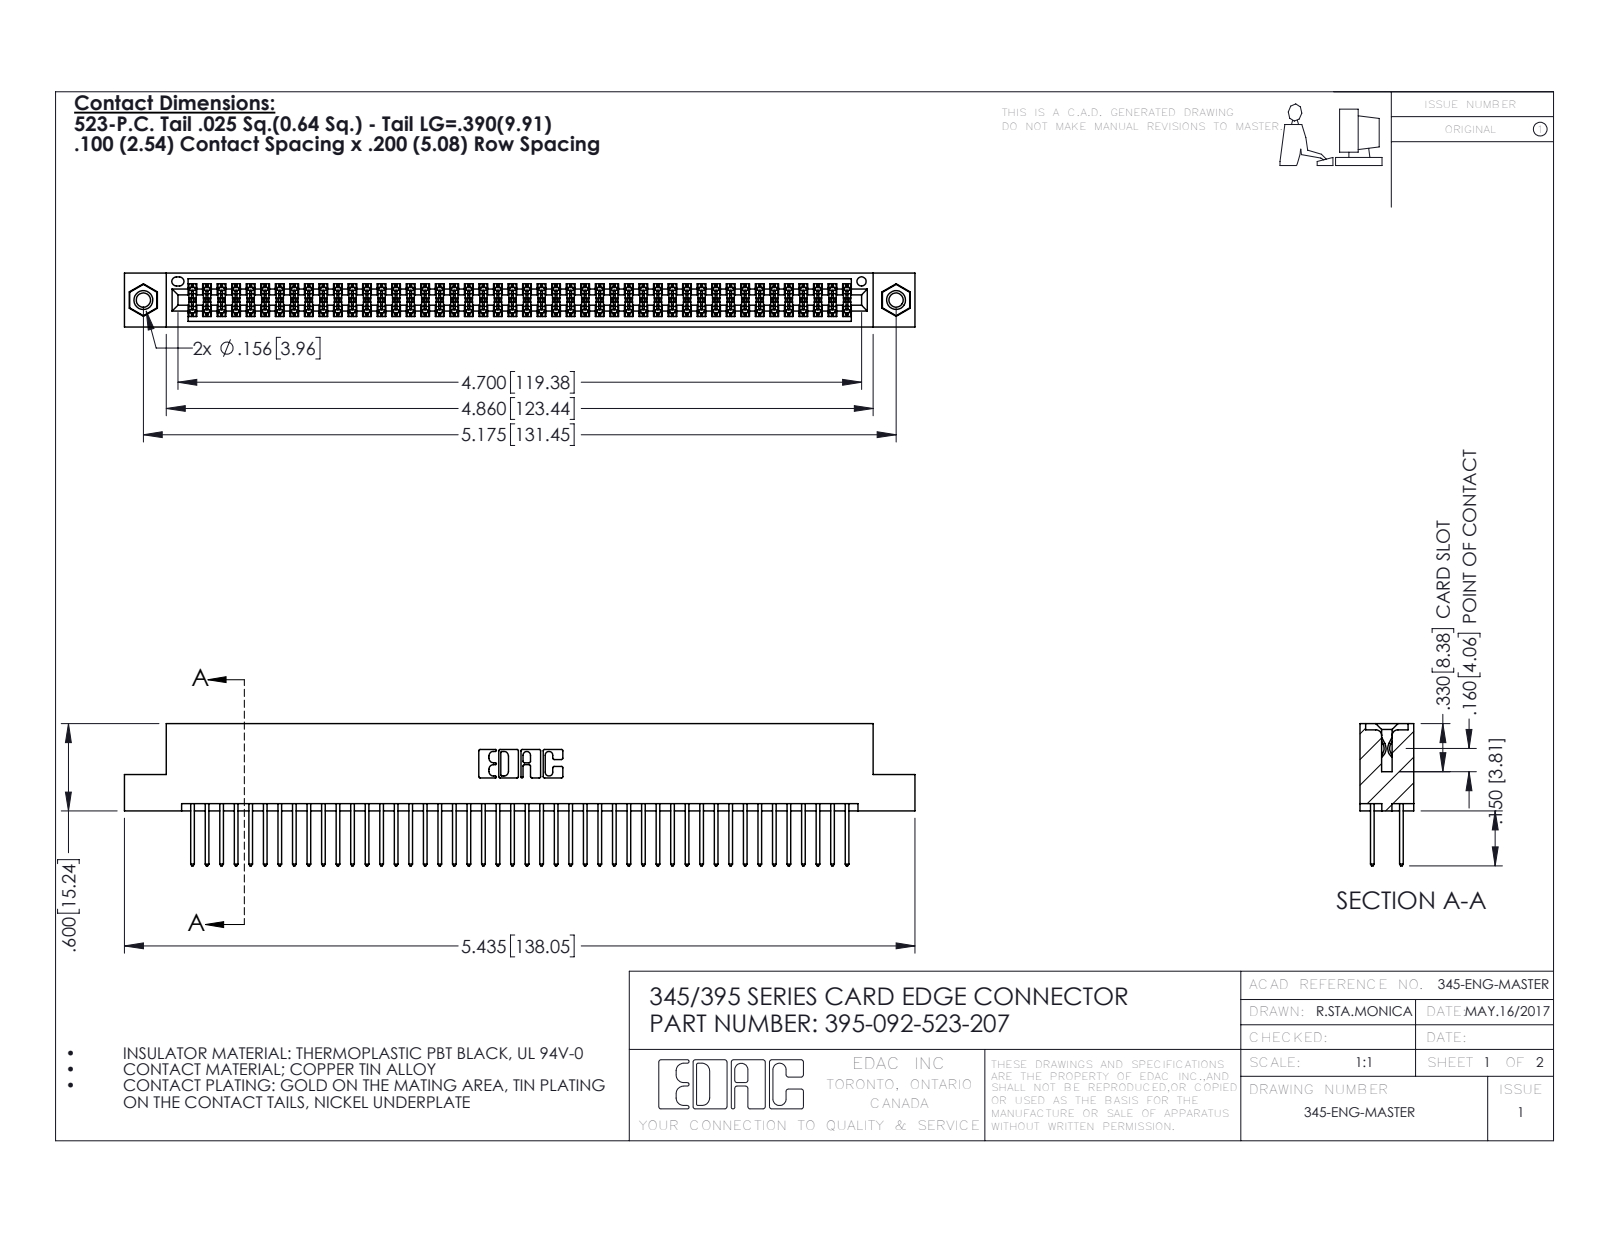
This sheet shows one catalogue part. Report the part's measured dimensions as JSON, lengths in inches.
{"part_name": "395-092-523-207; 345 Part_Flush Mounting Lugs - 0.156 Dia-TI; 345-292-001_345-293-123; 345-250-001_345-250-005-103", "step_written_by": "SolidWorks 2016 (CONFIG_CONTROL_DESIGN)", "units": "inches", "bodies": {"solids": 95, "faces": 4786, "planar": 3148, "cylindrical": 1622, "other": 16}, "overall_size": [5.435, 0.977, 0.37], "volume_in3": 0.831, "surface_area_in2": 32.69, "round_holes": [[0.098, 2], [0.125, 2], [0.156, 2], [0.064, 1]], "round_bosses_or_shafts": [[0.155, 2]], "partial_cylinders_radius": [[0.006, 138], [0.01, 92], [0.01, 22], [0.007, 6], [0.031, 6], [0.026, 3], [0.014, 2], [0.019, 2]], "face_to_face_distances": [0.072, 0.298, 0.2, 0.098, 0.272, 0.025, 0.37, 0.225, 0.175, 0.149], "hole_center_spacings": [0.27, 4.939, 5.175]}
